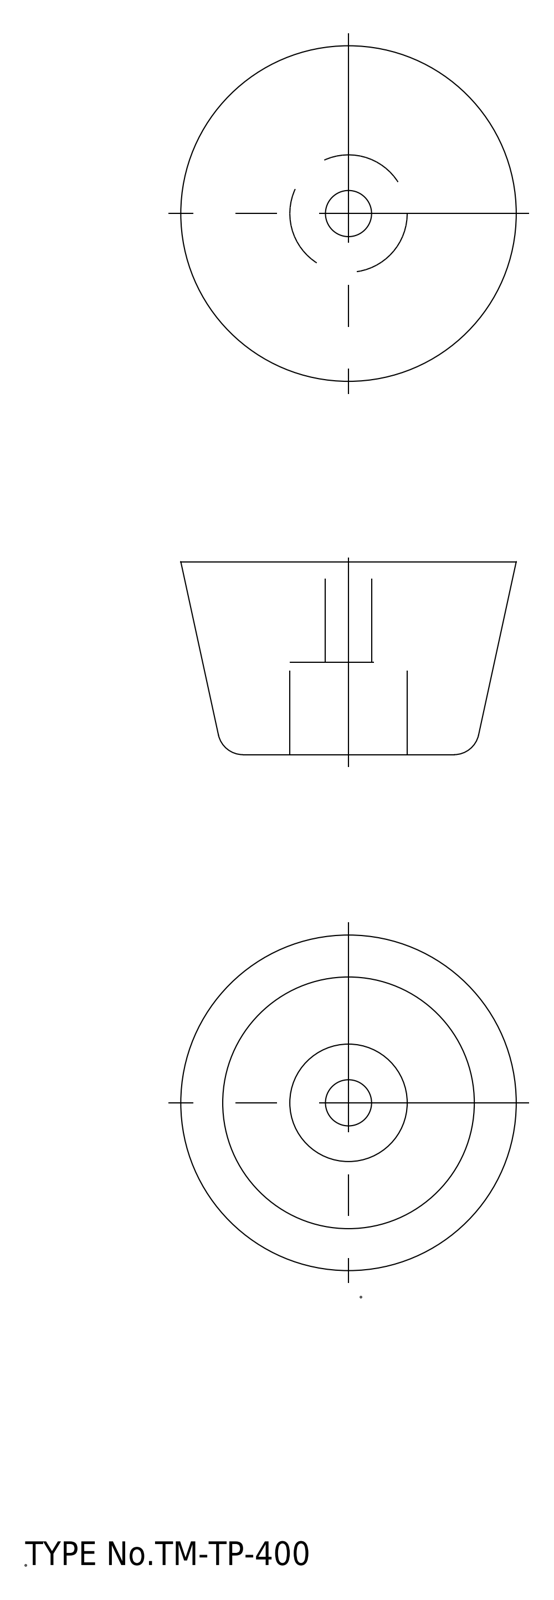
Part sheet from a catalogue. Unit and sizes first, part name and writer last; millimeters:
Units: millimetres
Overall size (bounding box): 40 × 40 × 23
Round holes (diameter × count): ⌀5.5 ×1, ⌀14 ×1
Main face-to-face distances: 23, 11, 12
Volume: 20 237 mm³ · Surface area: 5 124 mm²
Bodies: 1 solid, 11 faces (3 planar, 4 cylindrical, 4 other)
STEP written by: spGate 19.8.4 (****-****-****-****) (AUTOMOTIVE_DESIGN)
